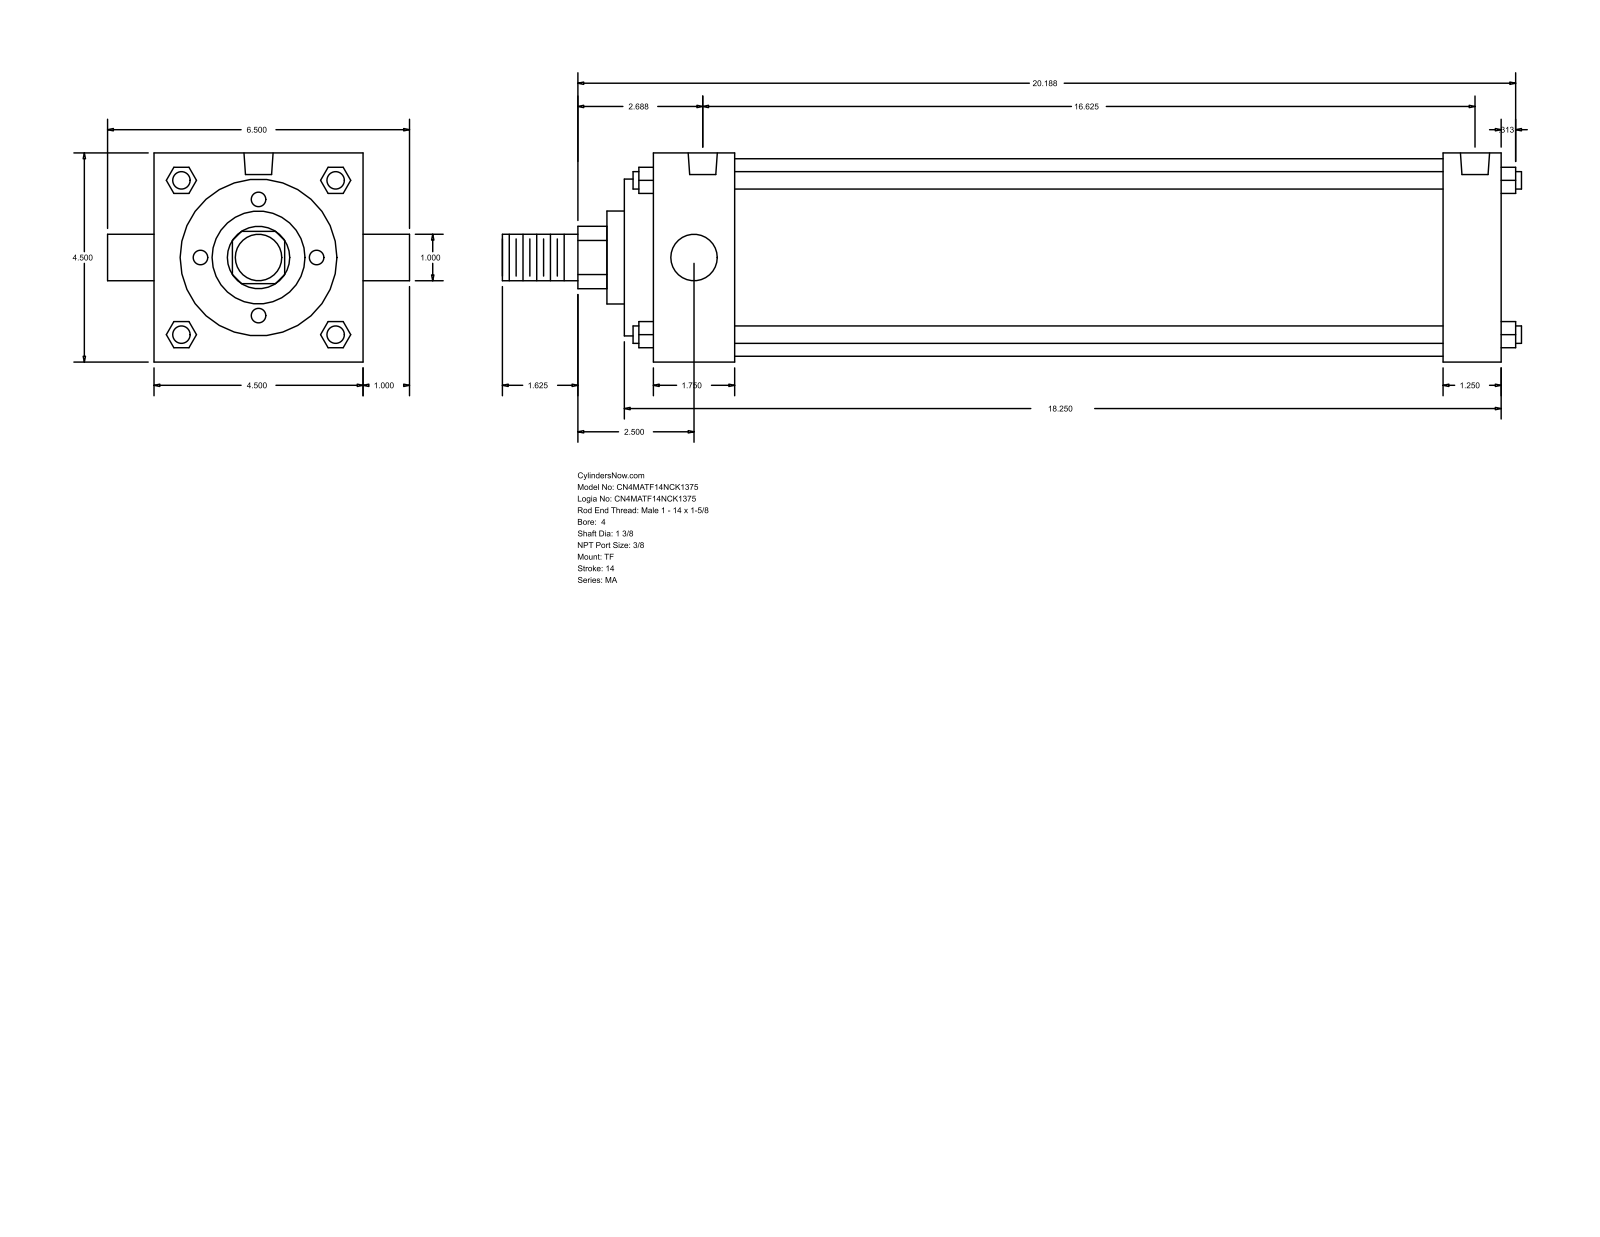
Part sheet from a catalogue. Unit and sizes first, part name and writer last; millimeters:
Units: millimetres
Overall size (bounding box): 557.21 × 165.1 × 114.3
Round holes (diameter × count): ⌀11.11 ×3, ⌀15.93 ×2
Round bosses / shafts (diameter × count): ⌀9.53 ×4, ⌀25.4 ×2, ⌀107.95 ×1, ⌀85.72 ×1, ⌀50.8 ×1, ⌀34.92 ×1
Partial cylindrical surfaces — rounded edges, fillets, slot ends (radius × count): R17.06 ×1
Main face-to-face distances: 114.3, 463.55, 479.42, 15.87, 447.67, 431.8, 31.75, 60.32, 44.45, 387.35
Hole centre spacings: 4.77, 417.51, 412.74, 422.28
Bodies: 0 solids, 122 faces (93 planar, 29 cylindrical, 0 other)
Part name (STEP PRODUCT): MA_TF__0400_1.375
STEP written by: GSSL Pune (CONFIG_CONTROL_DESIGN)
